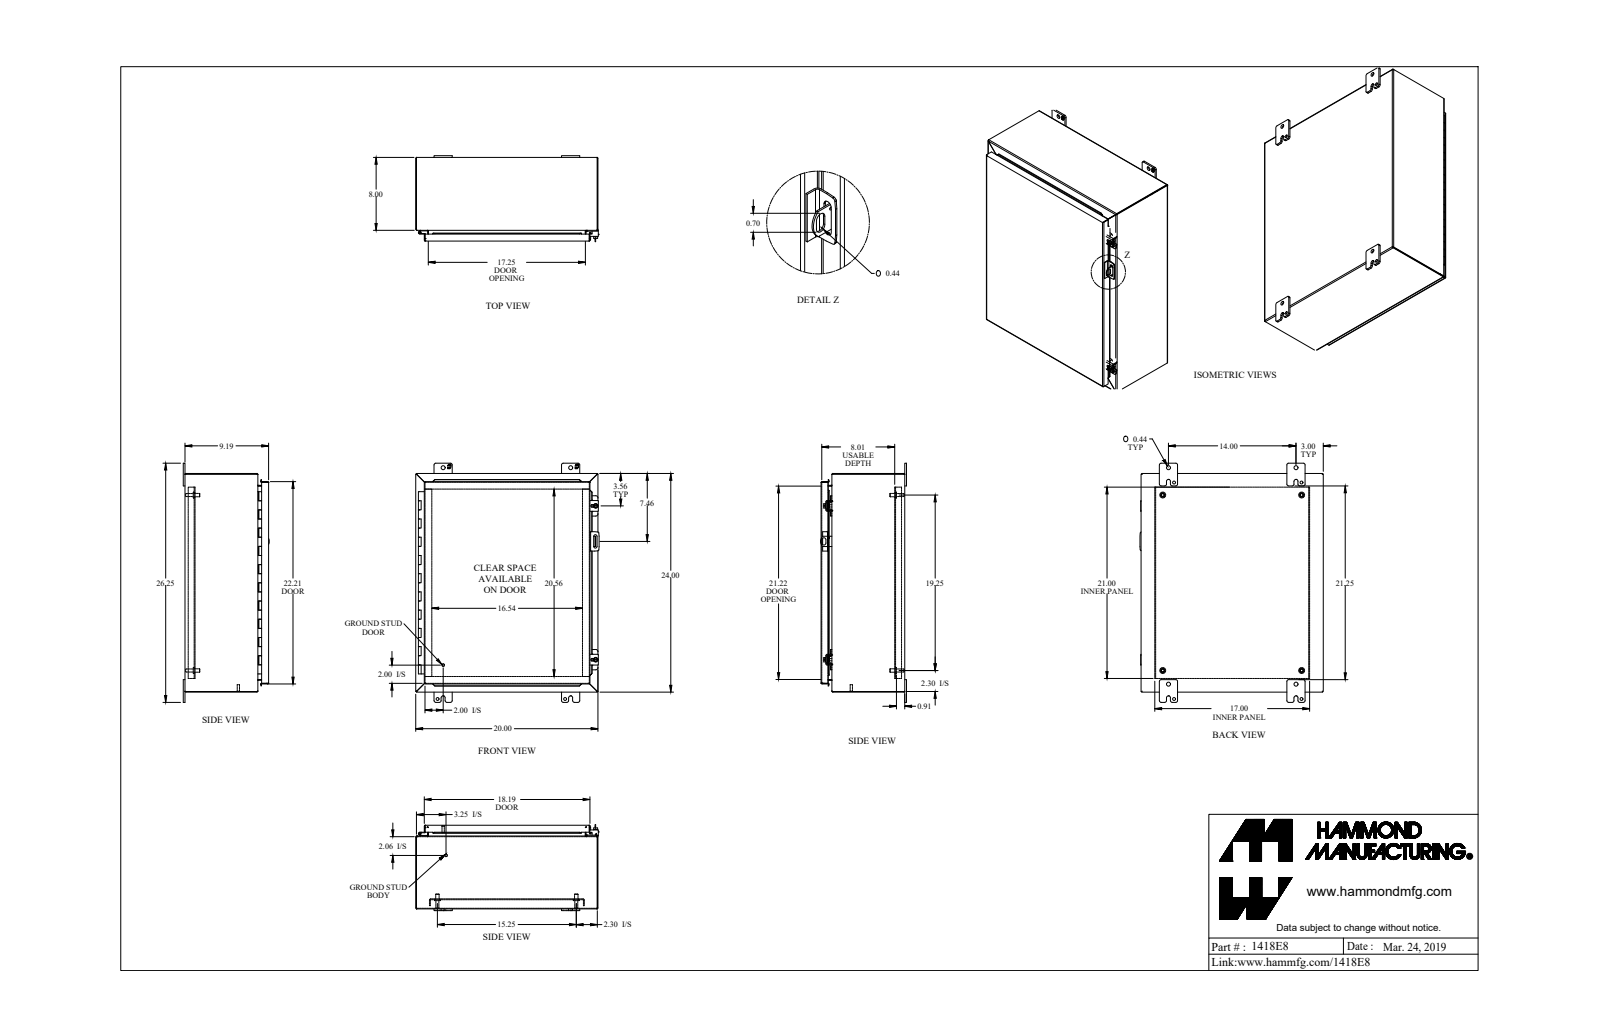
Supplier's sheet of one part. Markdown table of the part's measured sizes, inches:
| quantity | value |
| --- | --- |
| part name | 1418E8 |
| STEP written by | SolidWorks 2019 (AUTOMOTIVE_DESIGN) |
| units | inches |
| bodies | 38 solids, 1015 faces (698 planar, 263 cylindrical, 54 other) |
| overall size | 26.25 × 20.125 × 9.437 |
| volume | 179.4 in³ |
| surface area | 4 914 in² |
| round holes (diameter × count) | 0.313 × 4, 0.437 × 4, 0.5 × 4, 0.213 × 2, 0.265 × 2, 0.307 × 2, 0.375 × 2, 0.445 × 2, 0.125 × 1, 0.187 × 1 |
| round bosses / shafts (diameter × count) | 0.65 × 4, 0.375 × 4, 0.33 × 4, 1 × 2, 0.5 × 2, 0.39 × 2, 0.281 × 2, 0.25 × 2 |
| partial cylindrical surfaces (radius × count) | 0.188 × 26, 0.036 × 20, 0.108 × 20, 0.048 × 13, 0.143 × 13, 0.029 × 8, 0.045 × 8, 0.079 × 8 |
| main face-to-face distances | 0.072, 9.113, 0.05, 9.063, 9.135, 9.185, 0.095, 0.937, 19.928, 1.009 |
| hole center spacings | 24.559, 1.735, 14, 15.25, 23.75, 27.569, 1.625, 2.434 |
